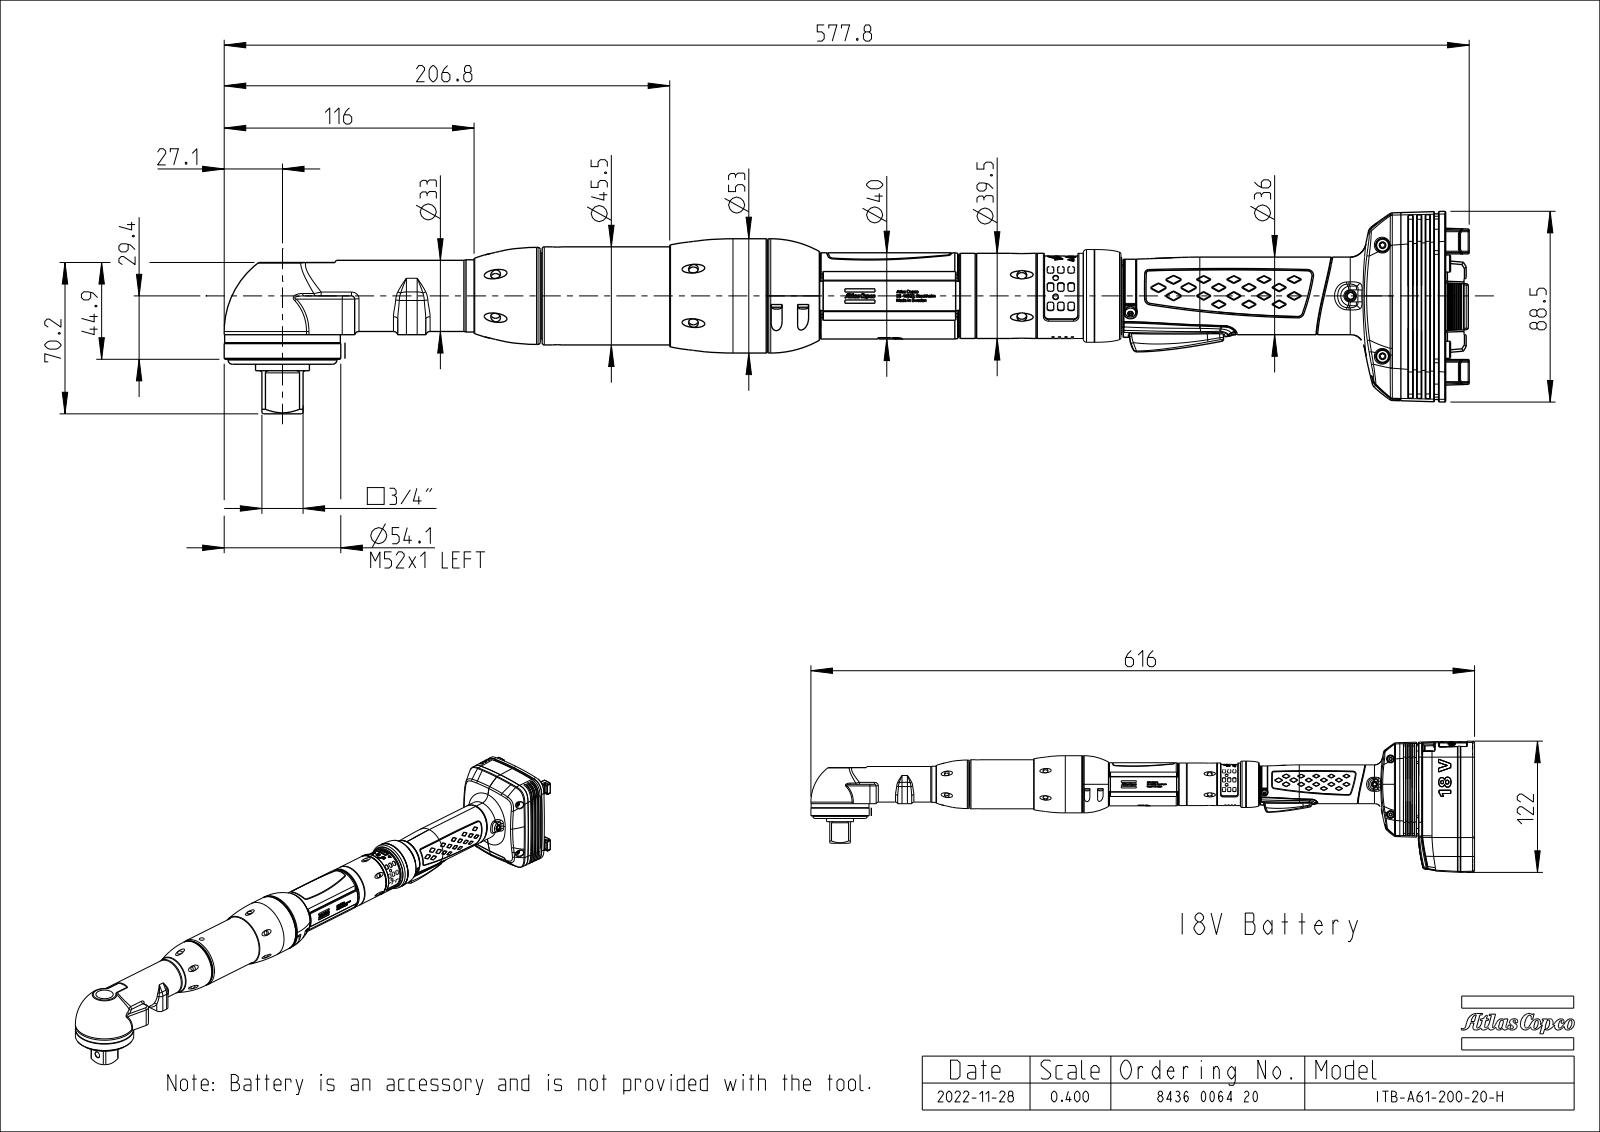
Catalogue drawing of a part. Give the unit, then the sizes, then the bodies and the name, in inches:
Units: inches
Overall size (bounding box): 22.766 × 3.699 × 2.935
Round holes (diameter × count): ⌀0.177 ×14, ⌀0.039 ×12, ⌀0.081 ×4, ⌀0.106 ×4, ⌀0.165 ×4, ⌀0.315 ×4, ⌀0.063 ×3, ⌀0.197 ×2, ⌀0.126 ×1, ⌀0.138 ×1, ⌀0.186 ×1, ⌀0.213 ×1
Round bosses / shafts (diameter × count): ⌀0.22 ×2, ⌀2.13 ×1, ⌀2.114 ×1, ⌀2.087 ×1, ⌀1.988 ×1, ⌀1.969 ×1, ⌀1.791 ×1, ⌀1.772 ×1
Partial cylindrical surfaces — rounded edges, fillets, slot ends (radius × count): R0.02 ×102, R0.039 ×60, R0.012 ×37, R0.079 ×30, R0.008 ×28, R0.009 ×18, R0.016 ×18, R0.011 ×12
Main face-to-face distances: 0.199, 0.079, 0.157, 0.622, 0.236, 1.037, 1.236, 0.539, 0.498, 0.697
Hole centre spacings: 0.118, 0.236, 0.748, 1.058, 0.354, 3.606, 6.02, 9.626
Volume: 57.7 in³ · Surface area: 189.7 in²
Bodies: 1 solid, 4893 faces (1462 planar, 1050 cylindrical, 2381 other)
Part name (STEP PRODUCT): EXT_COMP_SW0053
STEP written by: CREO PARAMETRIC BY PTC INC, 2020281 (CONFIG_CONTROL_DESIGN)
